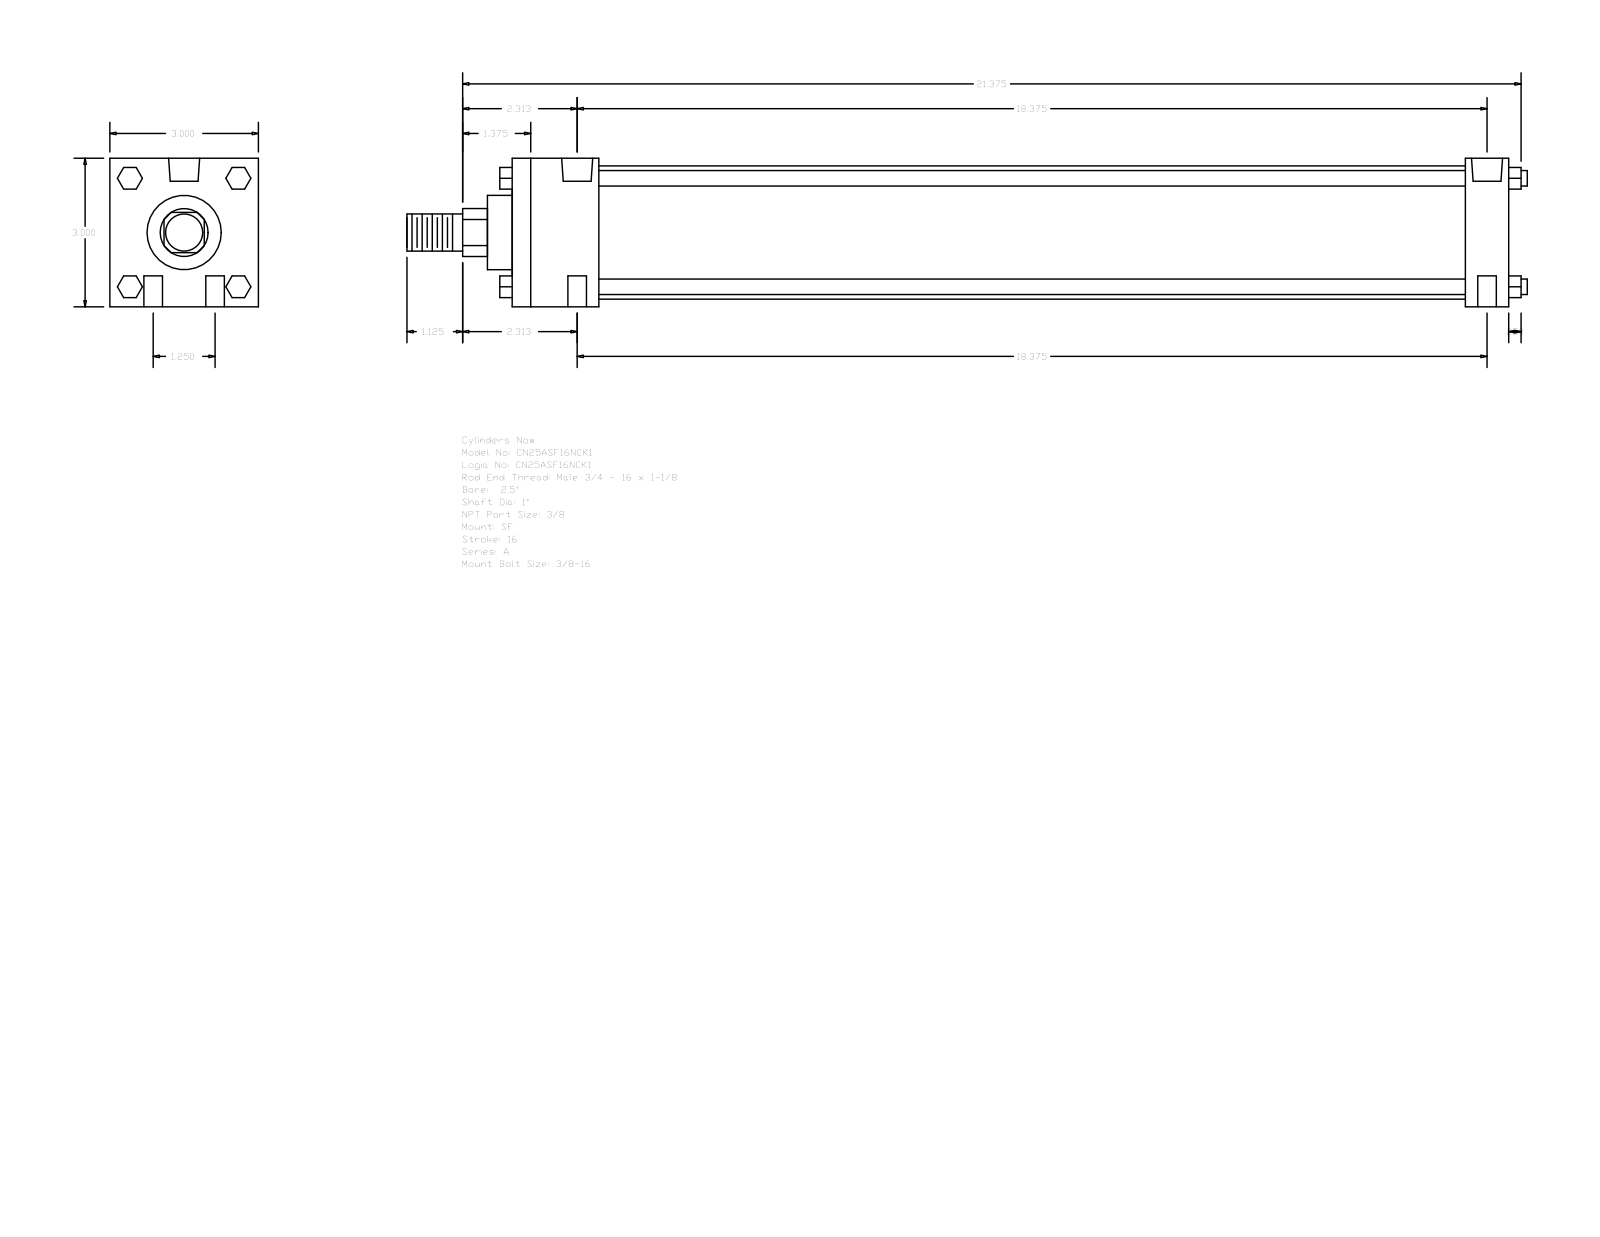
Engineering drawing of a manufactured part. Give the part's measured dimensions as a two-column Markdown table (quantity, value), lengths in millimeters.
| quantity | value |
| --- | --- |
| part name | A_SF__0250_1 |
| STEP written by | GSSL Pune (CONFIG_CONTROL_DESIGN) |
| units | millimeters |
| bodies | 0 solids, 124 faces (94 planar, 30 cylindrical, 0 other) |
| overall size | 574.67 × 76.2 × 76.2 |
| round holes (diameter × count) | 9.53 × 4, 5.56 × 2, 15.93 × 2 |
| round bosses / shafts (diameter × count) | 7.94 × 4, 68.33 × 1, 38.1 × 1, 25.4 × 1, 19.05 × 1 |
| partial cylindrical surfaces (radius × count) | 12.29 × 1 |
| main face-to-face distances | 76.2, 511.18, 488.95, 22.23, 44.45, 444.5, 466.73, 12.7, 11.11, 57.15 |
| hole center spacings | 15.88, 466.99, 466.72, 31.76, 467.8, 471.48 |
